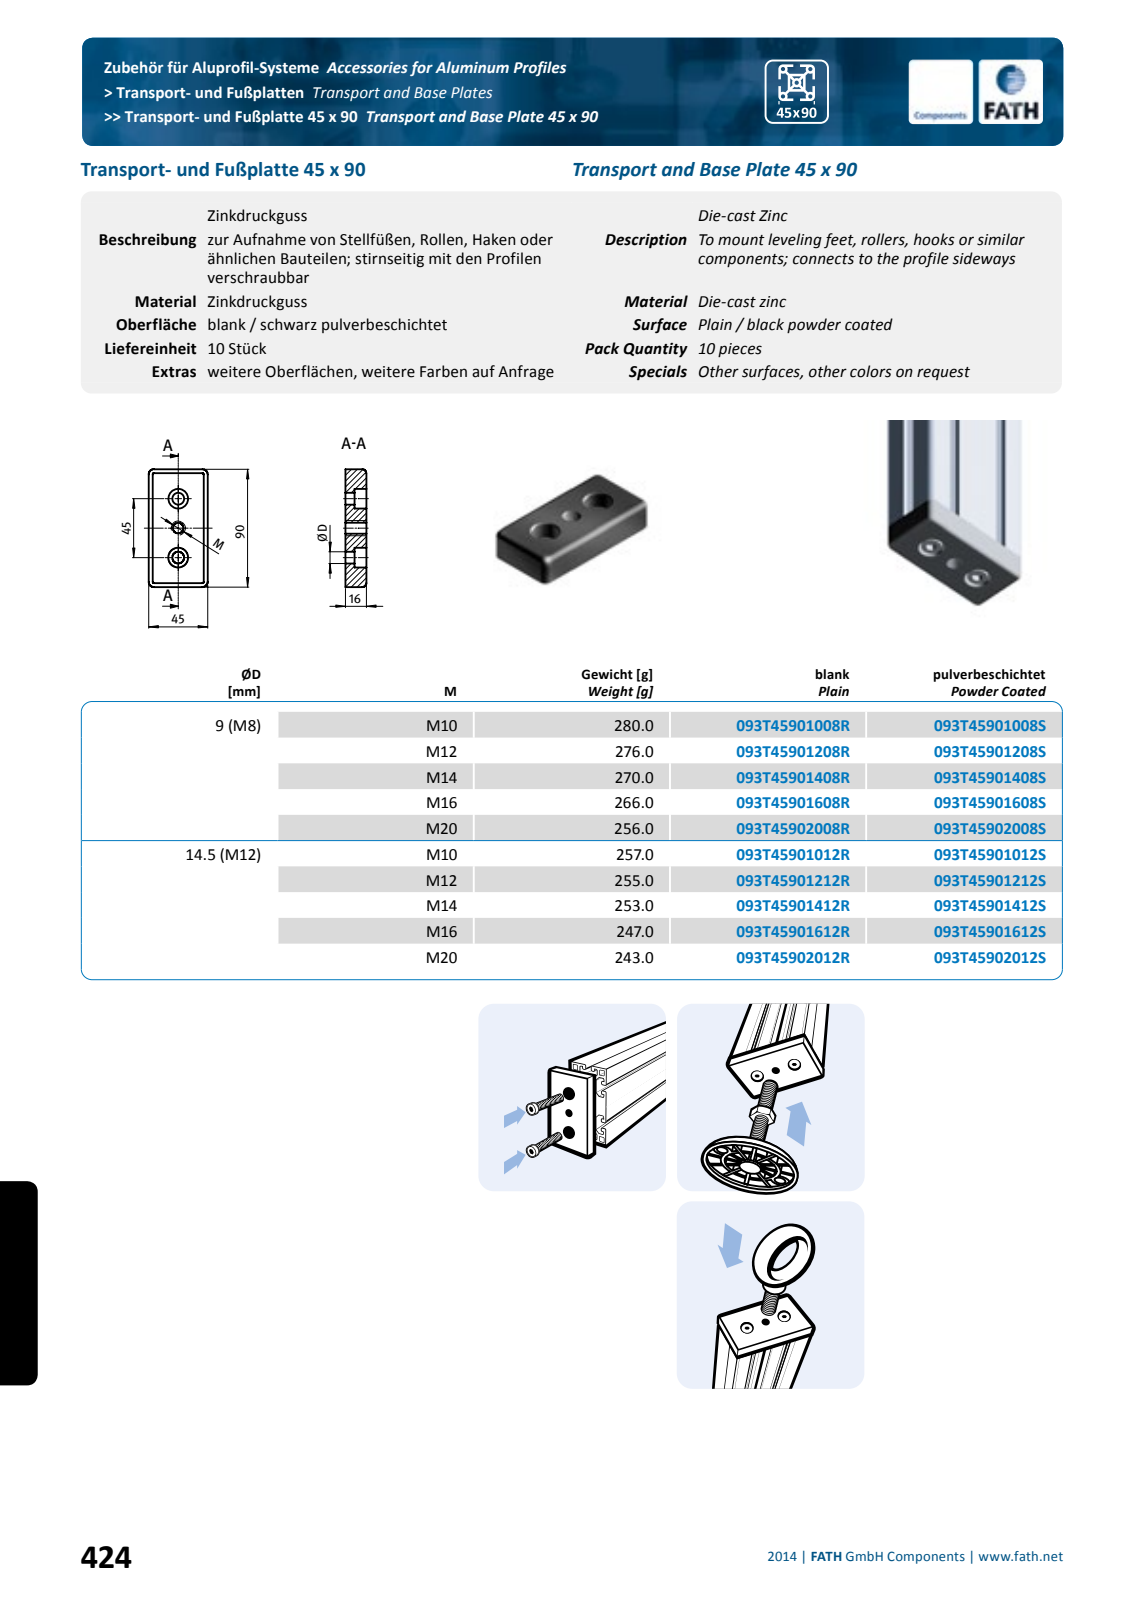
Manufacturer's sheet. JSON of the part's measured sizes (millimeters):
{"part_name": "fath_093t45901212s", "step_written_by": "Spatial InterOp 3D (automotive_design)", "units": "millimeters", "bodies": {"solids": 1, "faces": 224, "planar": 44, "cylindrical": 98, "other": 82}, "overall_size": [9000, 4500, 1600], "volume_mm3": 39310000000, "surface_area_mm2": 183300000, "round_holes": [[1450, 2], [2000, 2], [1010, 1]], "partial_cylinders_radius": [[100, 52], [300, 4], [400, 4], [1250, 2], [1400, 1]], "face_to_face_distances": [400, 1600, 4100, 4500, 1200, 2050, 3700, 8600, 800, 9000], "hole_center_spacings": [2250, 4500]}
